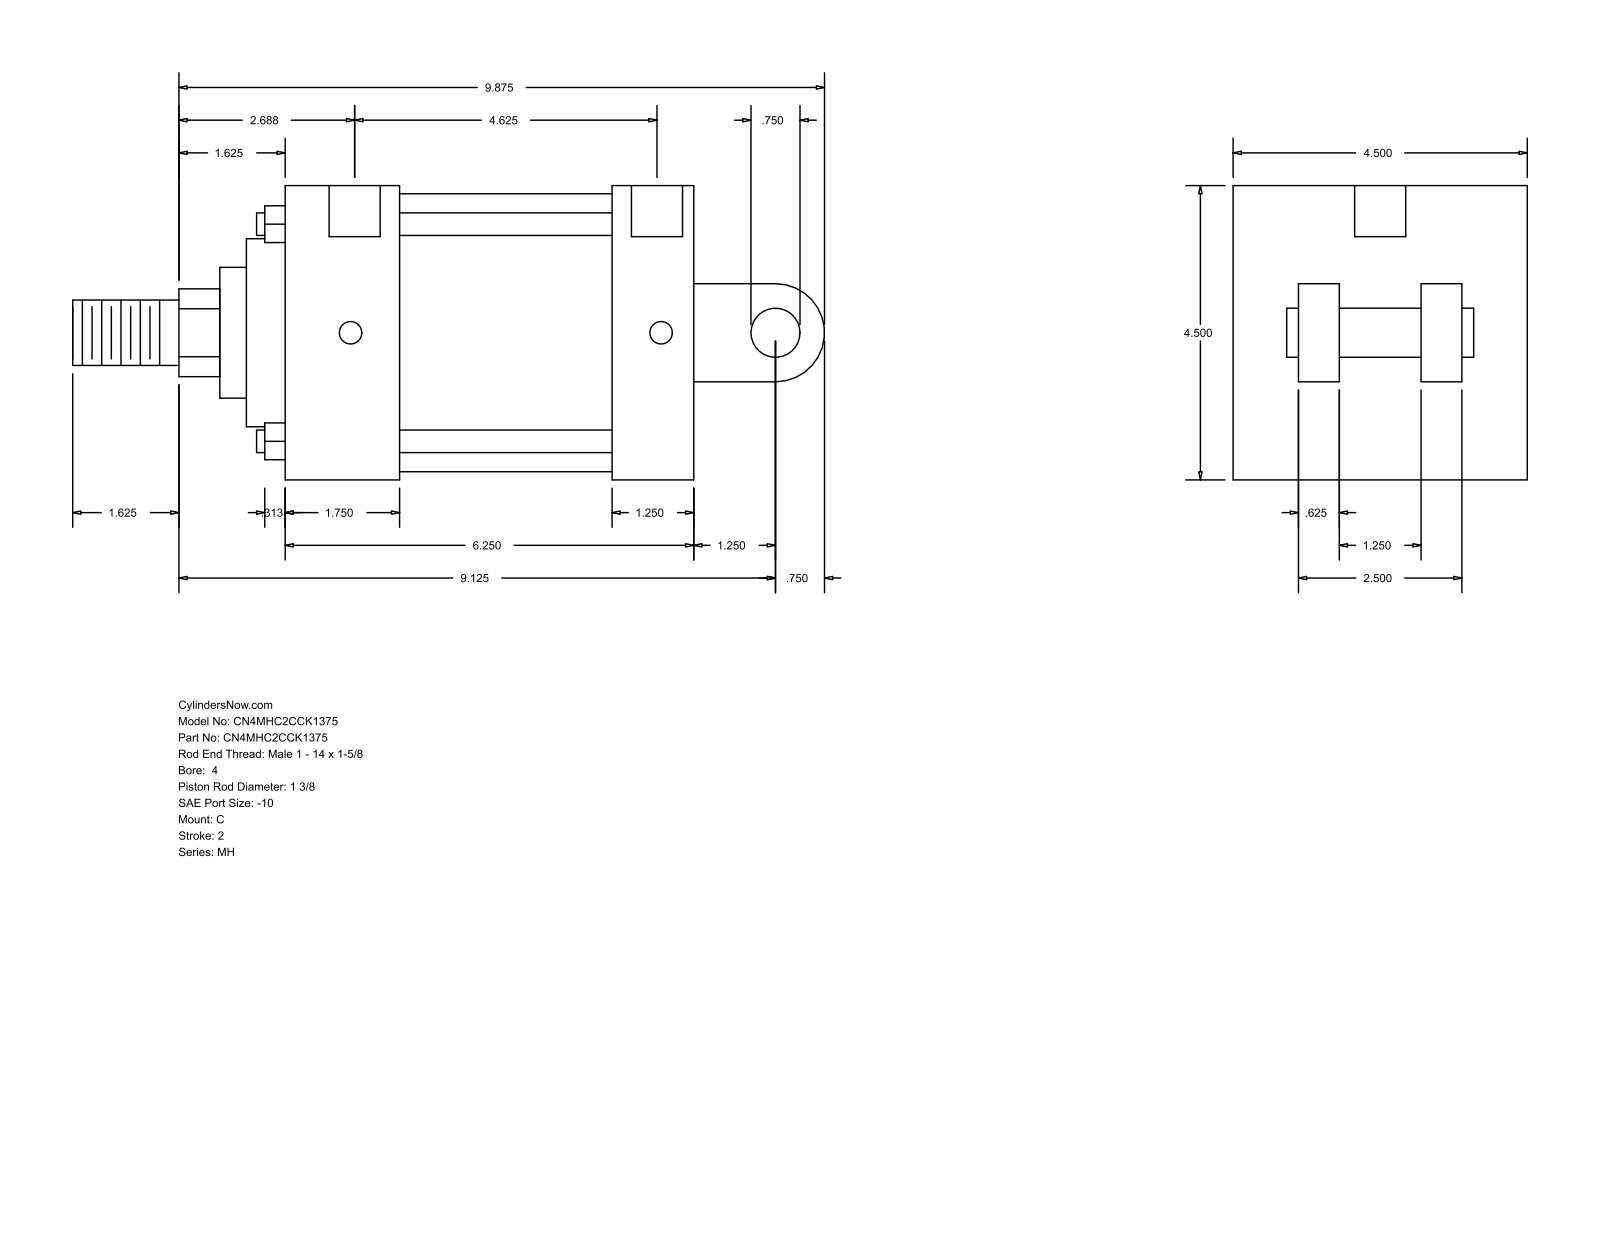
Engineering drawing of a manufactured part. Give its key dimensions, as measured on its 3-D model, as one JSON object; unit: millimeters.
{"part_name": "MH_C__0400_1.375", "step_written_by": "GSSL Pune (CONFIG_CONTROL_DESIGN)", "units": "millimeters", "bodies": {"solids": 0, "faces": 101, "planar": 71, "cylindrical": 30, "other": 0}, "overall_size": [292.1, 114.3, 114.3], "round_holes": [[8.73, 4], [19.84, 2]], "round_bosses_or_shafts": [[8.76, 4], [107.95, 1], [73.03, 1], [50.8, 1], [34.92, 1], [25.4, 1], [19.05, 1]], "partial_cylinders_radius": [[17.06, 1], [19.05, 1]], "face_to_face_distances": [114.3, 158.76, 44.45, 127.01, 82.56, 114.31, 31.75, 41.27, 73.03, 38.1], "hole_center_spacings": [120.65, 1.58, 1.59, 117.48, 119.06, 119.07]}
